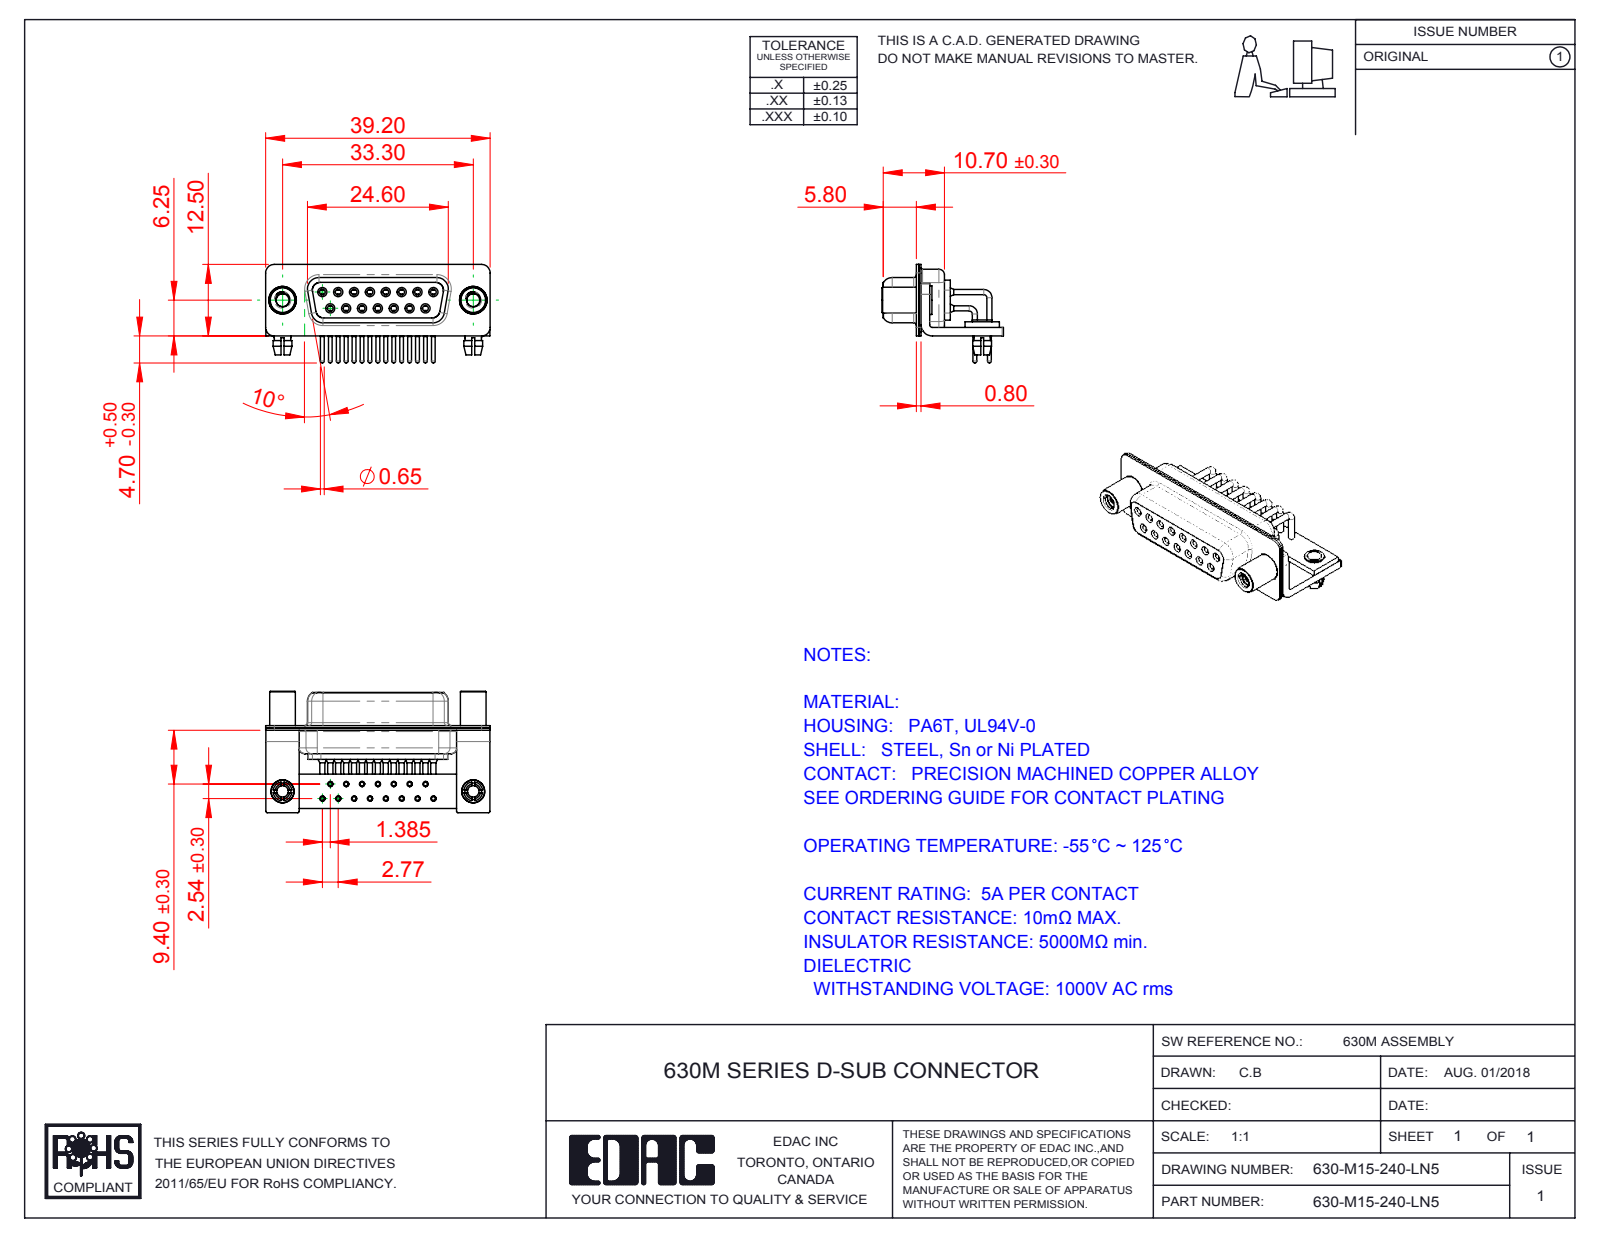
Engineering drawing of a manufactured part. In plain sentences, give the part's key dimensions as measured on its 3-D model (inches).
The part is named "630M Stabilizer Bracket; 630M Shell Rear_15 Contacts; 630M Shell Front_15 Contacts; 630M Housing_15 Contacts (+6 more)". Its 3-D file was written by "SolidWorks 2016 (CONFIG_CONTROL_DESIGN)". It is 25 solids with 1296 faces: 368 planar, 608 cylindrical and 320 other. Overall it measures 1.543 by 0.835 by 0.677 inches. Its volume is 0.196 cubic inches and its surface area 12.83 square inches. Round holes: 17 of diameter 0.079, 15 of diameter 0.035, 15 of diameter 0.039, 15 of diameter 0.043, 15 of diameter 0.067, 15 of diameter 0.071, 2 of diameter 0.089, 2 of diameter 0.098, 2 of diameter 0.126, 2 of diameter 0.157, 2 of diameter 0.189. Round bosses or shafts: 27 of diameter 0.035, 15 of diameter 0.063, 15 of diameter 0.059, 15 of diameter 0.026, 2 of diameter 0.197, 2 of diameter 0.193, 2 of diameter 0.177, 2 of diameter 0.157. Partial cylindrical surfaces (rounded edges, fillets, slot ends): 16 of radius 0.01, 16 of radius 0.059, 13 of radius 0.079, 8 of radius 0.053, 8 of radius 0.063, 5 of radius 0.02, 4 of radius 0.024, 4 of radius 0.026. The main face-to-face distances are 0.016, 0.091, 0.075, 0.031, 0.059, 0.368, 0.039, 0.057, 0.352, 0.033. The hole center spacings are 0.109, 0.218, 0.327, 0.124, 0.192, 0.436, 0.114, 0.29.
